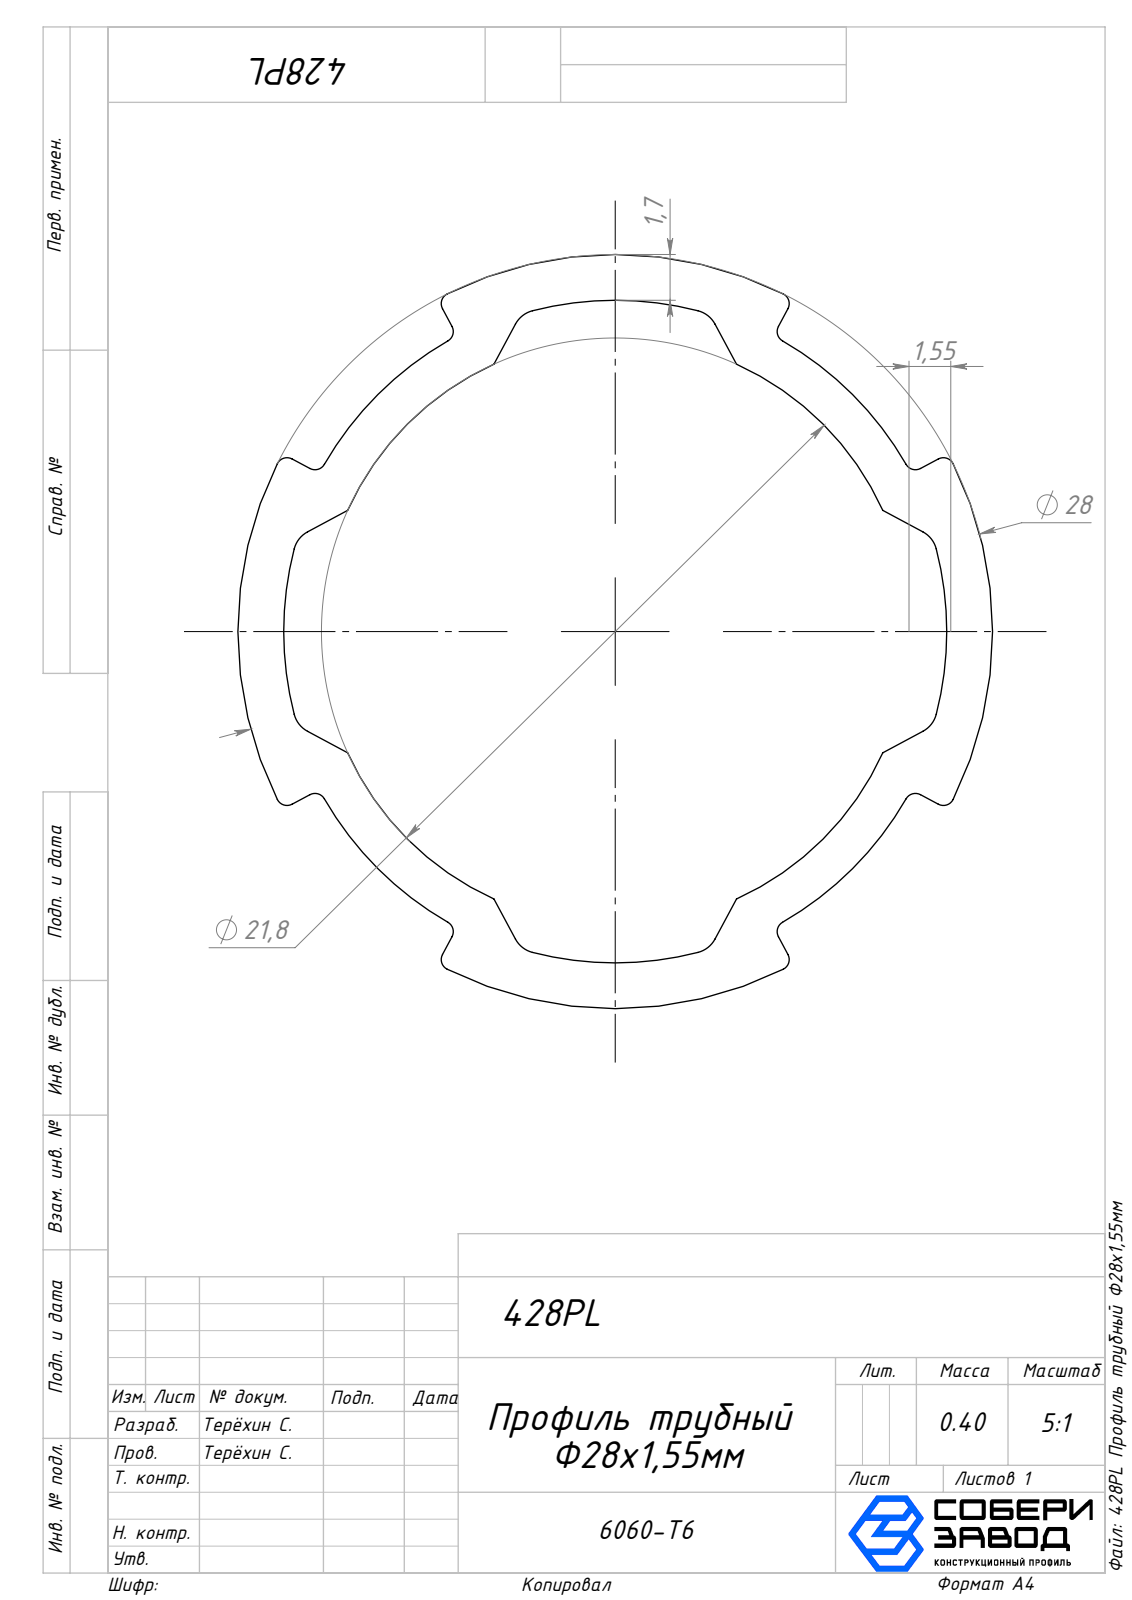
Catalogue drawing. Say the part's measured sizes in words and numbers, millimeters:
The part is named "428PL Профиль трубный Φ28х1,55мм_00; Сборка5". Its 3-D file was written by "SolidWorks 2024 (AUTOMOTIVE_DESIGN)". It is 1 solid with 64 faces: 18 planar, 46 cylindrical and 0 other. Overall it measures 1000 by 28 by 28 millimeters. Its volume is 148 751 cubic millimeters and its surface area 170 579 square millimeters. Partial cylindrical surfaces (rounded edges, fillets, slot ends): 16 of radius 0.4, 8 of radius 1, 1 of radius 10.9, 1 of radius 12.3, 1 of radius 12.45, 1 of radius 14. The main face-to-face distances are 17.32, 1000.
